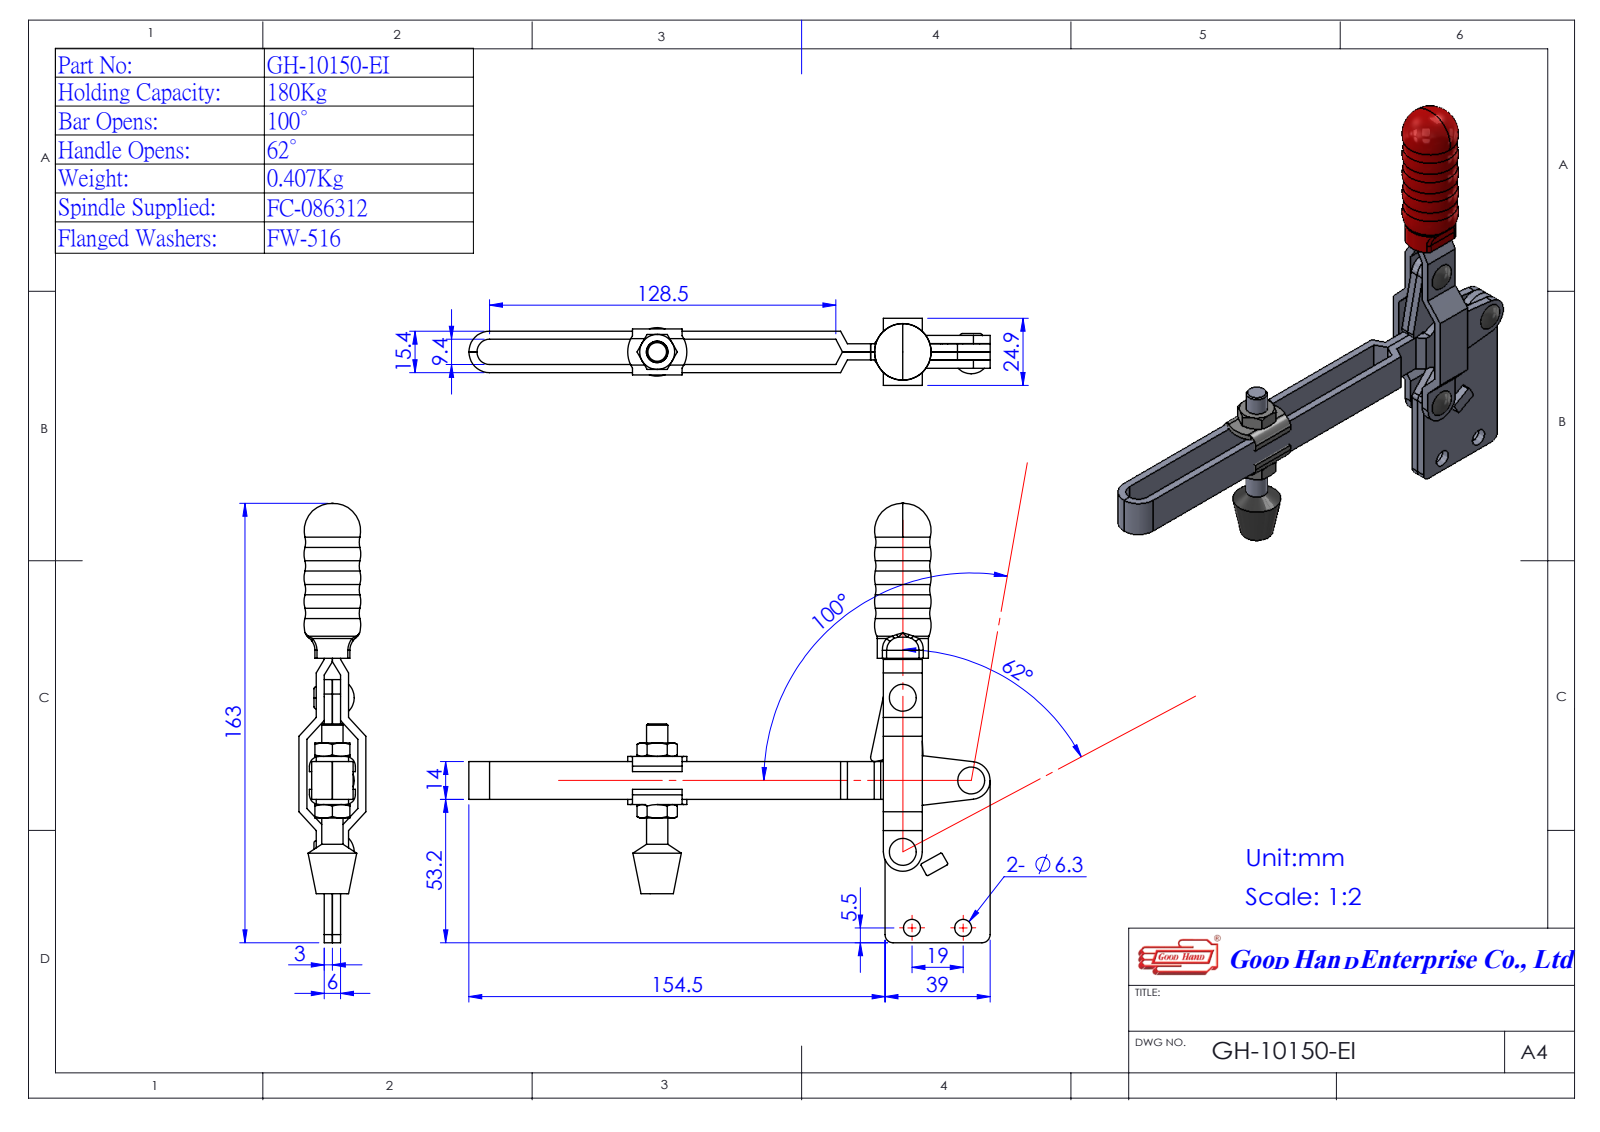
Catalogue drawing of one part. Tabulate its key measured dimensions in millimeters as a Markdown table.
| quantity | value |
| --- | --- |
| part name | Group5^GH-10150-EI(簡化)-1; Group6^GH-10150-EI(簡化)-1; 零件40^GH-10150-EI(簡化)-1; Group2^GH-10150-EI(簡化)-1 (+2 more) |
| STEP written by | SolidWorks 2016 (AUTOMOTIVE_DESIGN) |
| units | millimeters |
| bodies | 5 solids, 329 faces (140 planar, 95 cylindrical, 94 other) |
| overall size | 193.5 × 163.01 × 24.9 |
| volume | 66 456 mm³ |
| surface area | 36 311 mm² |
| round holes (diameter × count) | 5 × 4, 6.3 × 2 |
| round bosses / shafts (diameter × count) | 6.3 × 2, 7.93 × 1 |
| partial cylindrical surfaces (radius × count) | 0.5 × 4, 1.2 × 4, 2 × 4, 3 × 4, 3.6 × 4, 6 × 2, 6.75 × 2, 11.04 × 2 |
| main face-to-face distances | 3, 10.8, 1.6, 12.4, 6, 4.6, 7.8, 10.6, 1.8, 9.4 |
| hole center spacings | 19, 24.2, 26.53, 28.4, 30.72, 36.01, 36.71, 39.85 |
